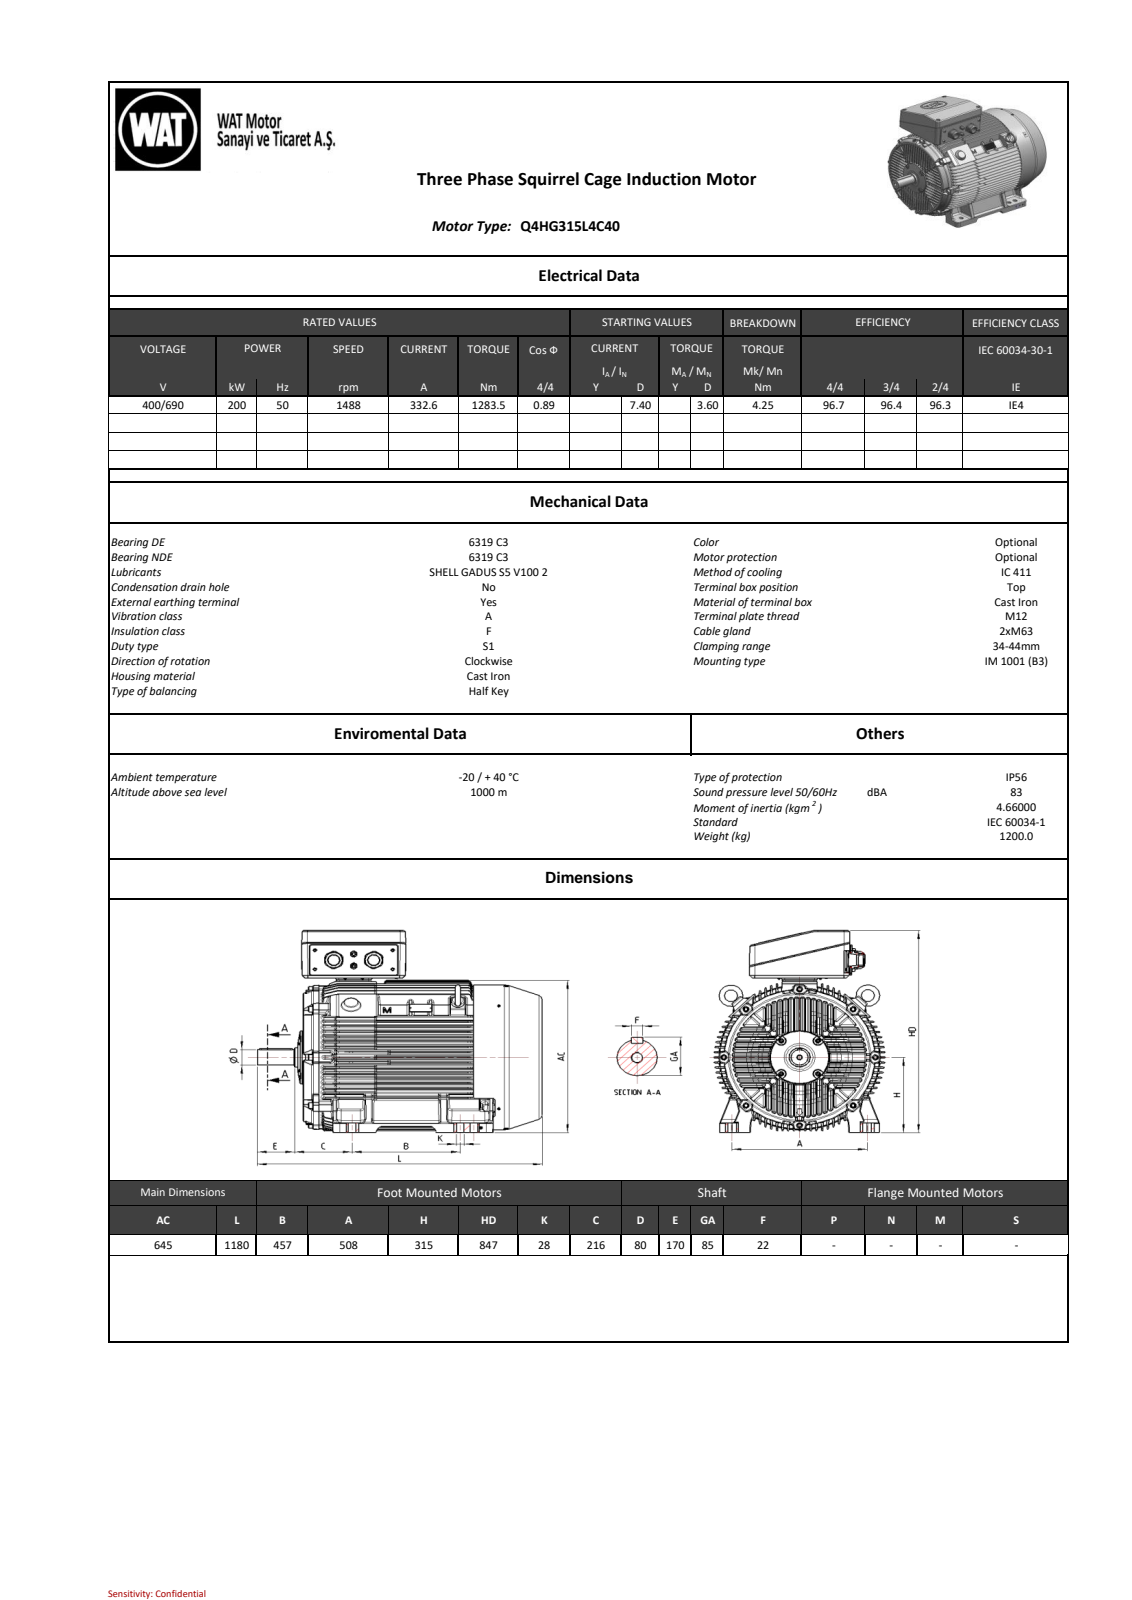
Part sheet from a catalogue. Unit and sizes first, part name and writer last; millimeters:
Units: millimetres
Overall size (bounding box): 1180 × 846.93 × 645
Round holes (diameter × count): ⌀20 ×8, ⌀8.5 ×3, ⌀8.8 ×2, ⌀9 ×2, ⌀10 ×2, ⌀12 ×2, ⌀21 ×2, ⌀44 ×2, ⌀44.4 ×2, ⌀4 ×1, ⌀5.3 ×1, ⌀8 ×1
Round bosses / shafts (diameter × count): ⌀24 ×8, ⌀20 ×8, ⌀16 ×8, ⌀10 ×4, ⌀64.8 ×2, ⌀50 ×2, ⌀607 ×1, ⌀565 ×1
Partial cylindrical surfaces — rounded edges, fillets, slot ends (radius × count): R6 ×726, R3 ×192, R1.5 ×152, R2.09 ×59, R2.61 ×54, R0.8 ×35, R15 ×34, R10 ×24
Main face-to-face distances: 20.8, 263.64, 20.71, 305.15, 242.75, 221.95, 41.69, 20.89, 41.51, 284.35
Hole centre spacings: 79.06, 150, 79.05, 0.33, 819, 30, 50, 50.01
Bodies: 0 solids, 8526 faces (3301 planar, 1824 cylindrical, 3401 other)
Part name (STEP PRODUCT): 26009910674F4pz6
STEP written by: SIEMENS PLM Software NX 11.0 (AUTOMOTIVE_DESIGN)
